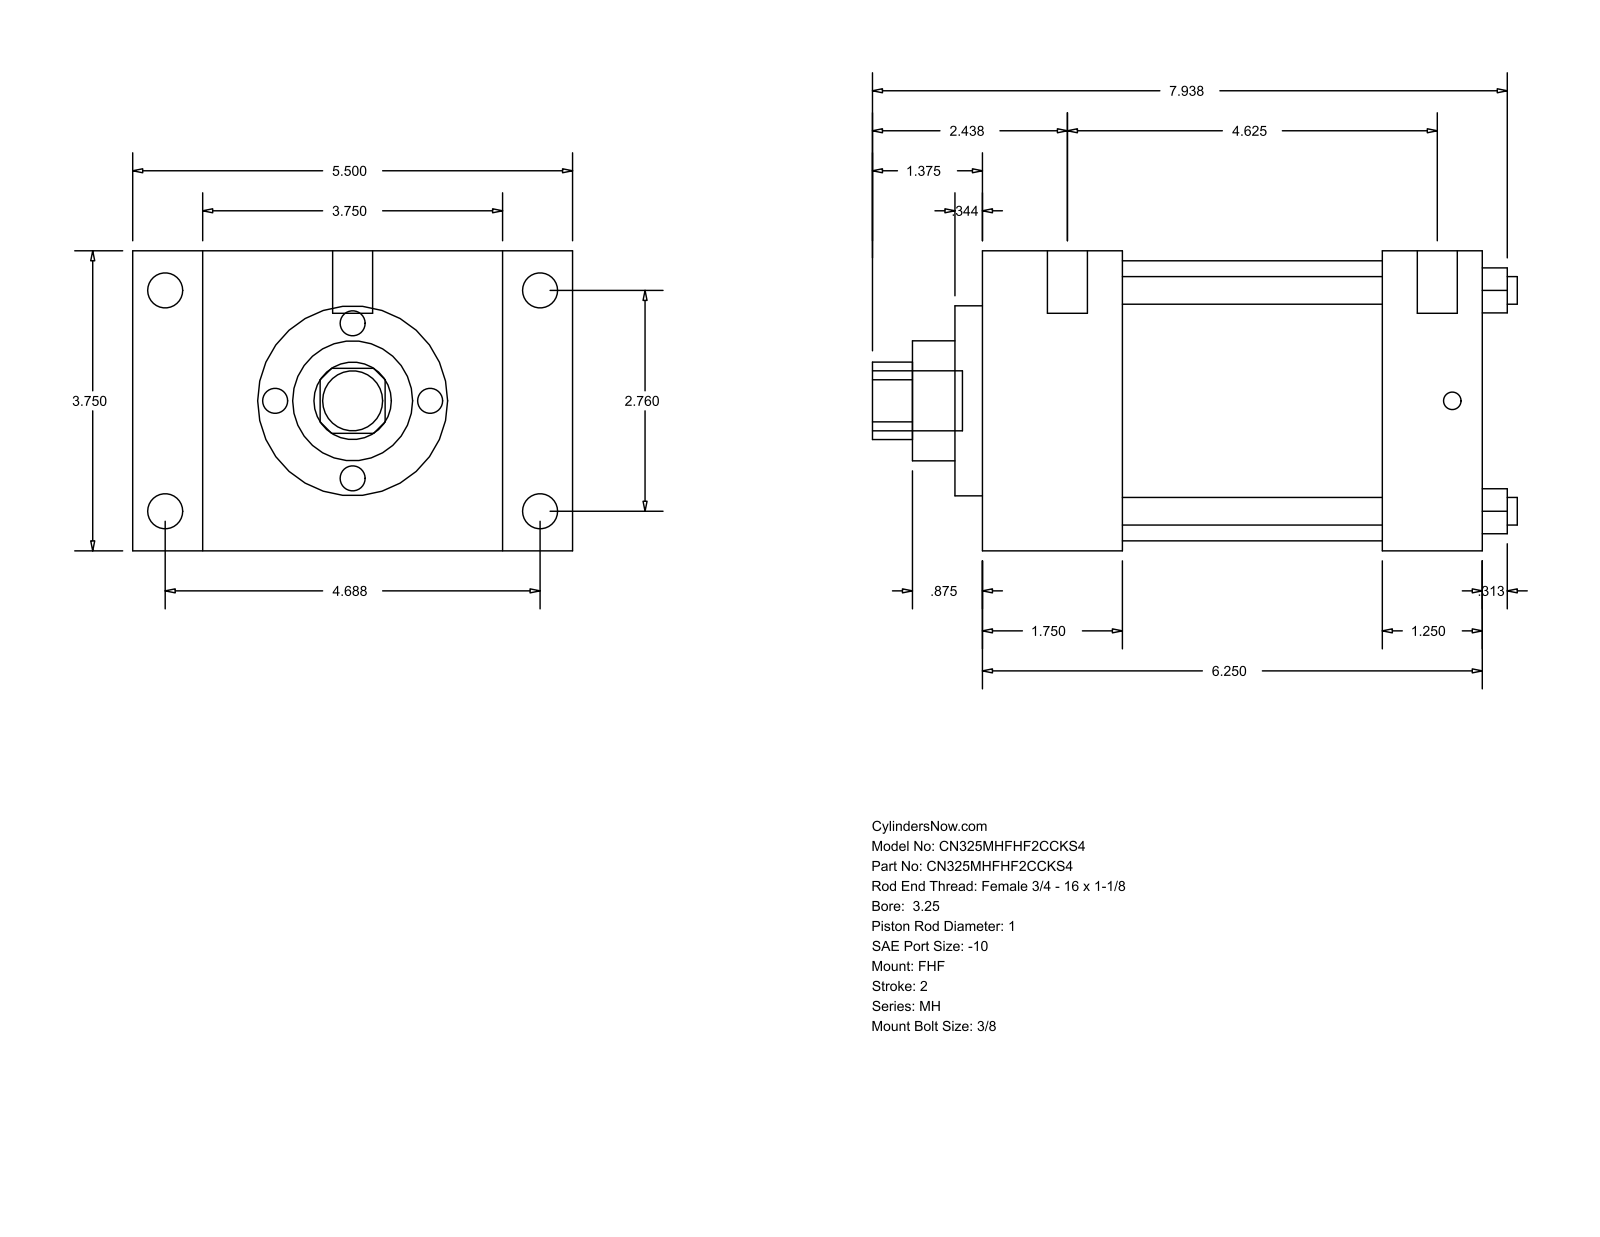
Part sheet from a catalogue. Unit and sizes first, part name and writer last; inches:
Units: inches
Overall size (bounding box): 8.063 × 5.5 × 3.75
Round holes (diameter × count): ⌀0.345 ×4, ⌀1 ×1, ⌀1.5 ×1, ⌀2.375 ×1, ⌀3.5 ×1
Round bosses / shafts (diameter × count): ⌀0.438 ×4, ⌀0.219 ×4, ⌀0.5 ×2, ⌀0.75 ×1
Partial cylindrical surfaces — rounded edges, fillets, slot ends (radius × count): R0.484 ×1
Main face-to-face distances: 3.75, 6.25, 1.75, 4.5, 0.875, 4.625, 5.5, 5, 3.25, 1.25
Hole centre spacings: 1.952, 2.76, 3.903
Bodies: 0 solids, 90 faces (61 planar, 29 cylindrical, 0 other)
Part name (STEP PRODUCT): MH_FHF__0325_1
STEP written by: GSSL Pune (CONFIG_CONTROL_DESIGN)
